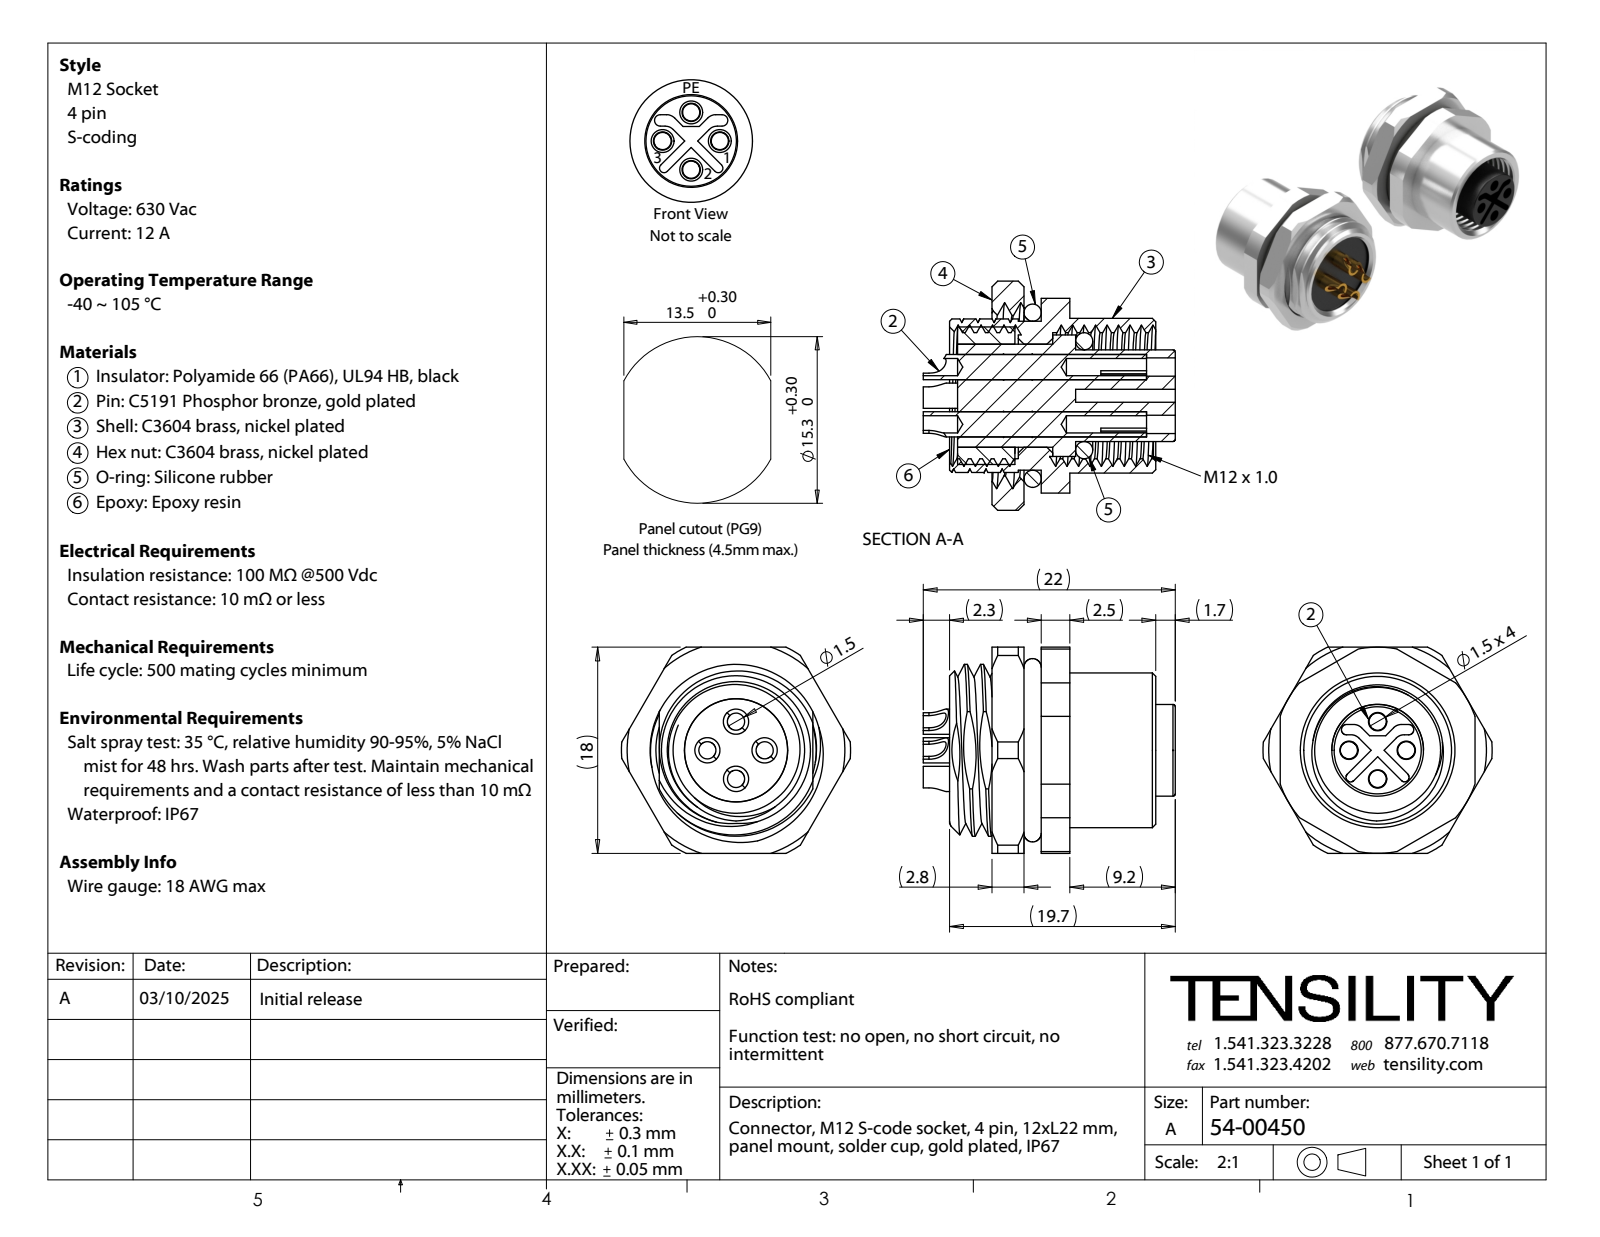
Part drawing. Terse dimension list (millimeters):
name: 54-00450-02; 54-00450-03; 54-00450-01; 54-00450-06 (+3 more)
written by: SolidWorks 2021 (CONFIG_CONTROL_DESIGN)
unit: mm
bodies: 10 solids, 338 faces (109 planar, 145 cylindrical, 84 other)
size: 22 × 20 × 18
volume: 2 716 mm³; area: 5 976 mm²
holes: 4× ⌀1.5, 4× ⌀1.6, 1× ⌀9, 1× ⌀11, 1× ⌀14
bosses: 4× ⌀2.2, 1× ⌀13.5, 1× ⌀13, 1× ⌀12, 1× ⌀10.6, 1× ⌀8
rounds: 4× R1, 2× R0.4, 2× R0.45, 2× R1.86, 1× R7.5, 1× R9, 1× R10
face distances: 3, 2.5, 7.3, 0.8, 5.3, 2, 1.5, 0.5, 9.8, 2.3
hole spacings: 2.5, 3.54, 5
